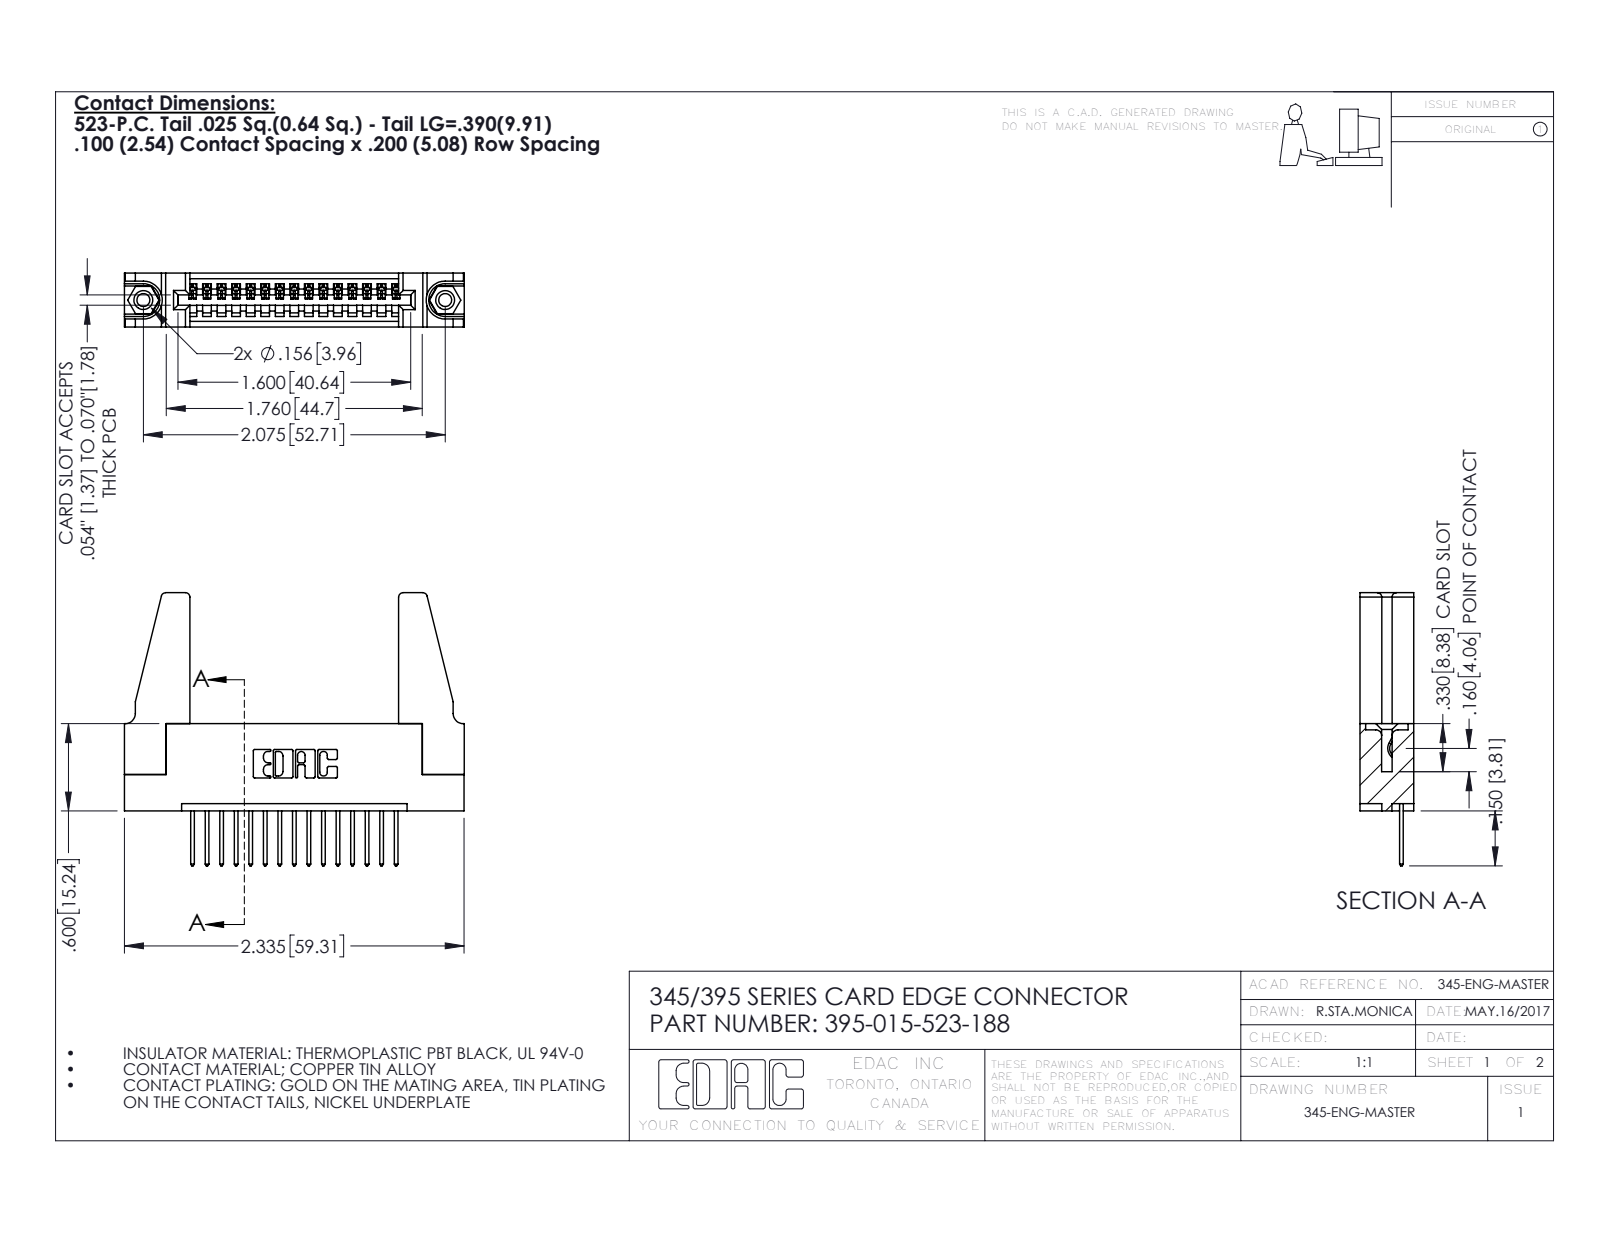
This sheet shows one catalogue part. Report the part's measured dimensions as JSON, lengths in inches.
{"part_name": "345-250-001_345-250-001-102; 345 Part_Flush Mounting Lugs - 0.156 Dia-TH; 345-292-001_345-293-123; 345-220-078_345-220-088 (+1 more)", "step_written_by": "SolidWorks 2016 (CONFIG_CONTROL_DESIGN)", "units": "inches", "bodies": {"solids": 20, "faces": 1120, "planar": 752, "cylindrical": 352, "other": 16}, "overall_size": [2.336, 1.877, 0.37], "volume_in3": 0.529, "surface_area_in2": 15.45, "round_holes": [[0.089, 2], [0.125, 2], [0.156, 2], [0.064, 1]], "round_bosses_or_shafts": [[0.155, 2]], "partial_cylinders_radius": [[0.006, 30], [0.01, 30], [0.01, 22], [0.03, 8], [0.007, 6], [0.031, 6], [0.026, 3], [0.031, 2]], "face_to_face_distances": [0.37, 0.072, 0.298, 0.2, 0.098, 0.272, 0.025, 0.225, 0.148, 0.15], "hole_center_spacings": [0.27, 1.842, 2.075]}
